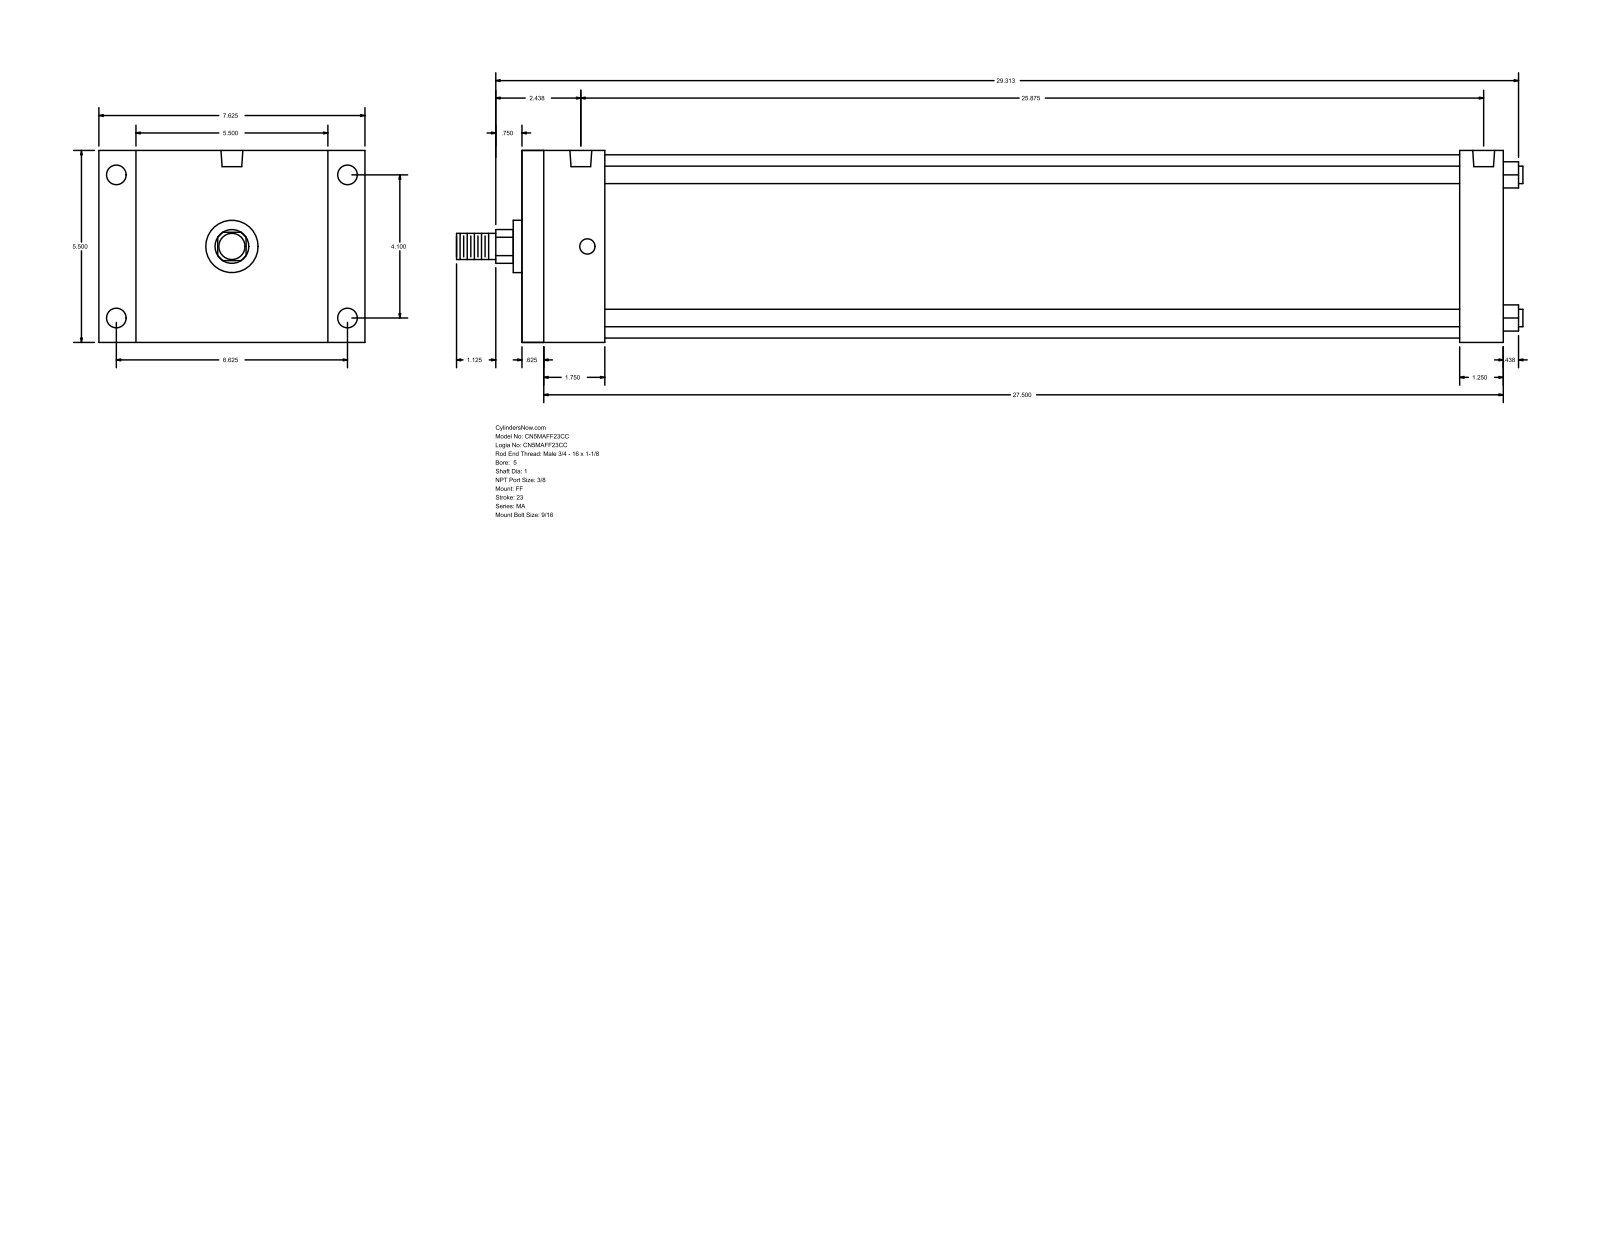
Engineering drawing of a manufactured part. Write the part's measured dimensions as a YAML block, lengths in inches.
part_name: "MA_FF__0500_1"
step_written_by: "GSSL Pune (CONFIG_CONTROL_DESIGN)"
units: inches
bodies: {solids: 0, faces: 92, planar: 64, cylindrical: 28, other: 0}
overall_size: [30.563, 7.625, 5.5]
round_holes:
  - {diameter: 0.437, count: 4}
  - {diameter: 0.563, count: 4}
  - {diameter: 0.627, count: 2}
round_bosses_or_shafts:
  - {diameter: 0.5, count: 4}
  - {diameter: 5.25, count: 1}
  - {diameter: 1.5, count: 1}
  - {diameter: 1, count: 1}
  - {diameter: 0.75, count: 1}
partial_cylinders:
  - {radius: 0.484, count: 1}
face_to_face_distances: [5.5, 28.125, 0.625, 27.5, 26.875, 26.25, 1.25, 2.375, 1.75, 24.5]
hole_center_spacings: [0.187, 4.1, 6.625, 7.791, 25.5, 25.688, 25.875]
